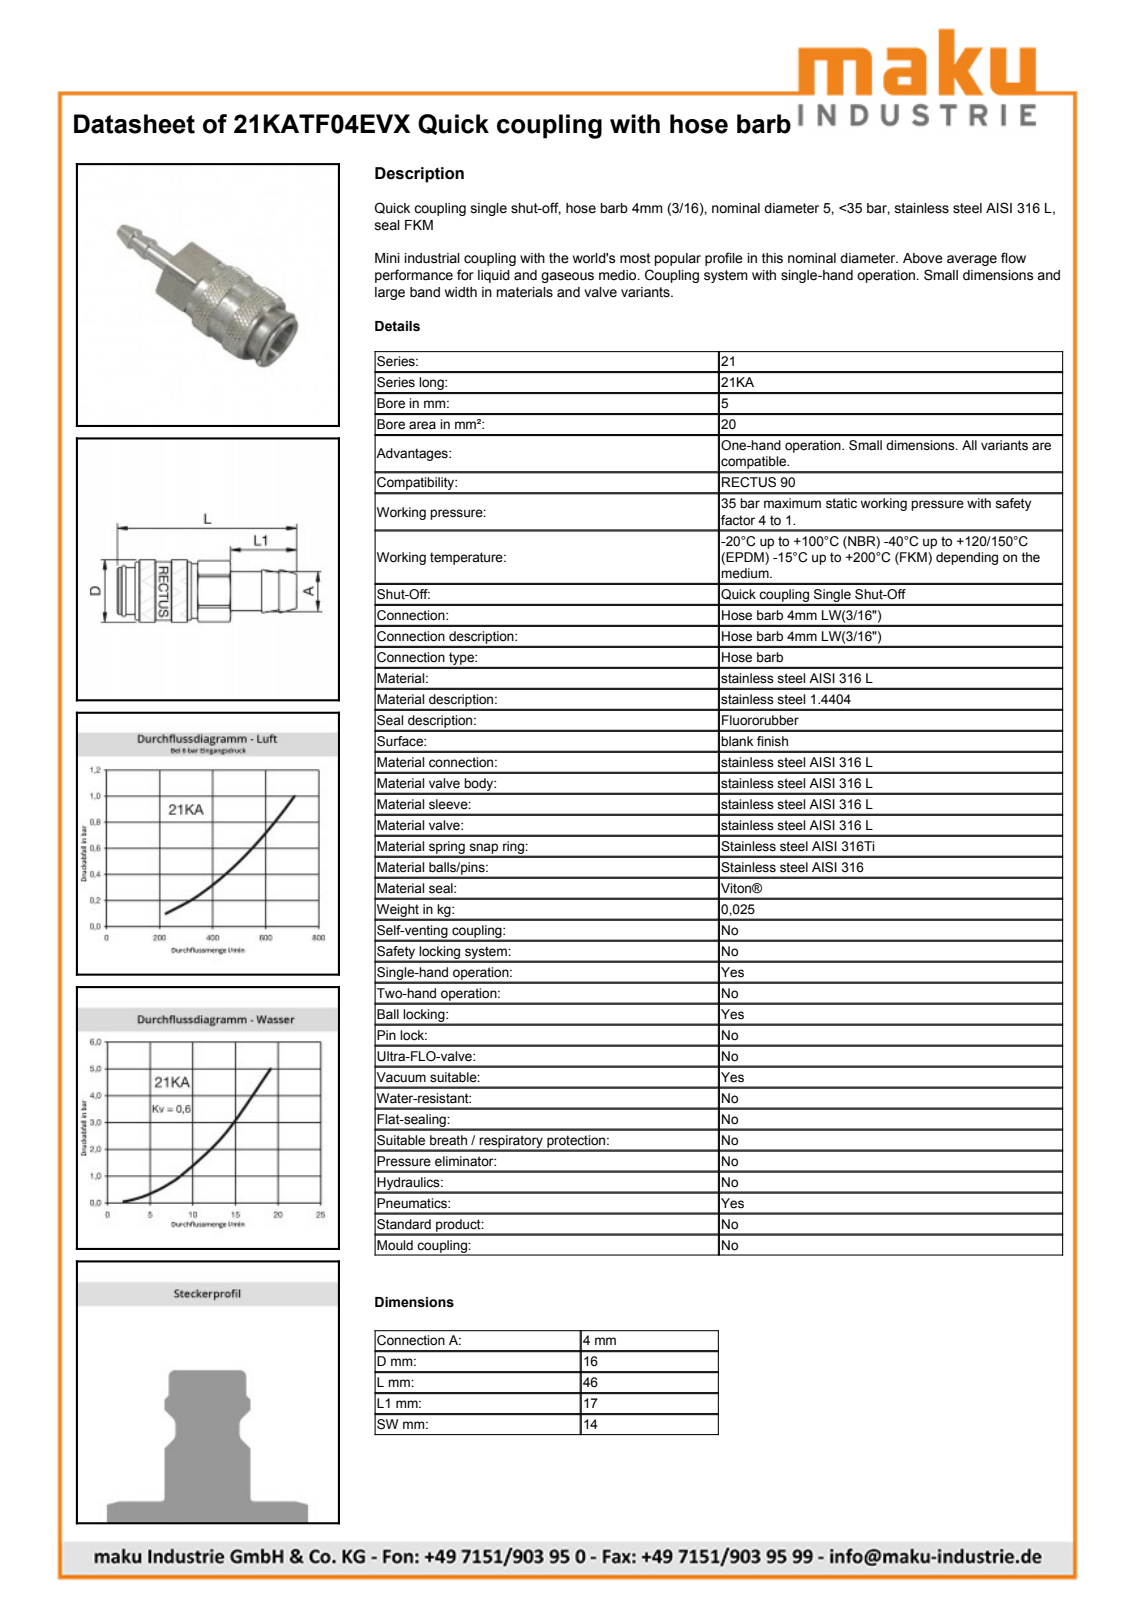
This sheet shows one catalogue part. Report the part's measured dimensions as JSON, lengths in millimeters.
{"part_name": "D105804", "step_written_by": "Autodesk Inventor 2013 (AUTOMOTIVE_DESIGN)", "units": "millimeters", "bodies": {"solids": 2, "faces": 402, "planar": 164, "cylindrical": 63, "other": 175}, "overall_size": [46.15, 16.15, 16.15], "volume_mm3": 4917, "surface_area_mm2": 3397, "round_holes": [[12.15, 1], [14, 1]], "round_bosses_or_shafts": [[16.15, 1], [15.1, 1], [12, 1], [11.4, 1], [11.15, 1], [4.05, 1]], "partial_cylinders_radius": [[5.5, 1], [7.45, 1], [7.9, 1]], "face_to_face_distances": [14, 29.15, 11.55, 16.15, 13, 4.6, 24.55, 11.9, 7.3, 4.25]}
